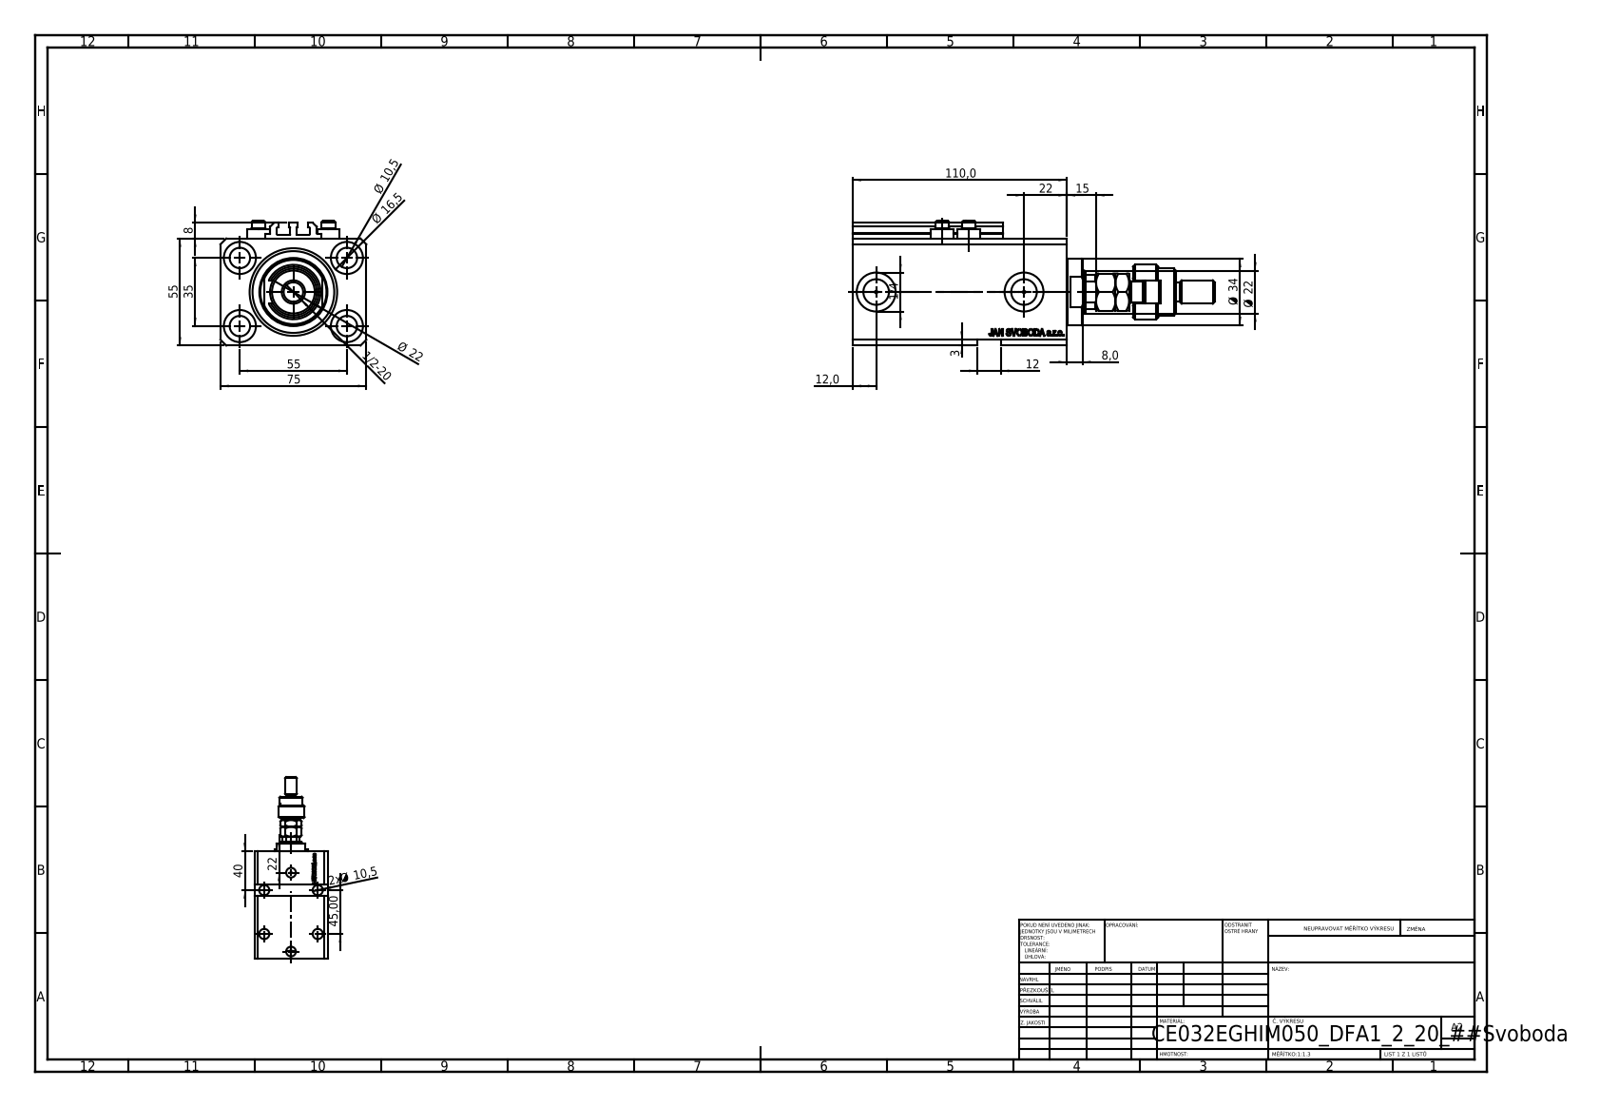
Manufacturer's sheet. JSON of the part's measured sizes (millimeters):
{"part_name": "V250CE_E_Body; V250CE_C_VCP; MFA; ALLEN BOLT V250CE (+2 more)", "step_written_by": "SolidWorks 2019 (CONFIG_CONTROL_DESIGN)", "units": "millimeters", "bodies": {"solids": 10, "faces": 1169, "planar": 542, "cylindrical": 159, "other": 468}, "overall_size": [186, 75, 64], "volume_mm3": 399218, "surface_area_mm2": 102764, "round_holes": [[10.5, 9], [1.25, 4], [4, 4], [16.5, 4], [10, 2], [13.16, 2], [20, 2], [22, 1], [32, 1], [45, 1]], "round_bosses_or_shafts": [[11.6, 4], [7, 4], [34, 1], [28, 1], [24, 1], [18, 1], [12, 1], [11, 1]], "partial_cylinders_radius": [[0.2, 10], [9.75, 1], [10.5, 1]], "face_to_face_distances": [55, 75, 15, 110, 3, 95, 9.9, 8, 19, 85.1], "hole_center_spacings": [32.6, 32.87, 55, 68.74, 13.6, 14.09, 23.05, 25.81]}
